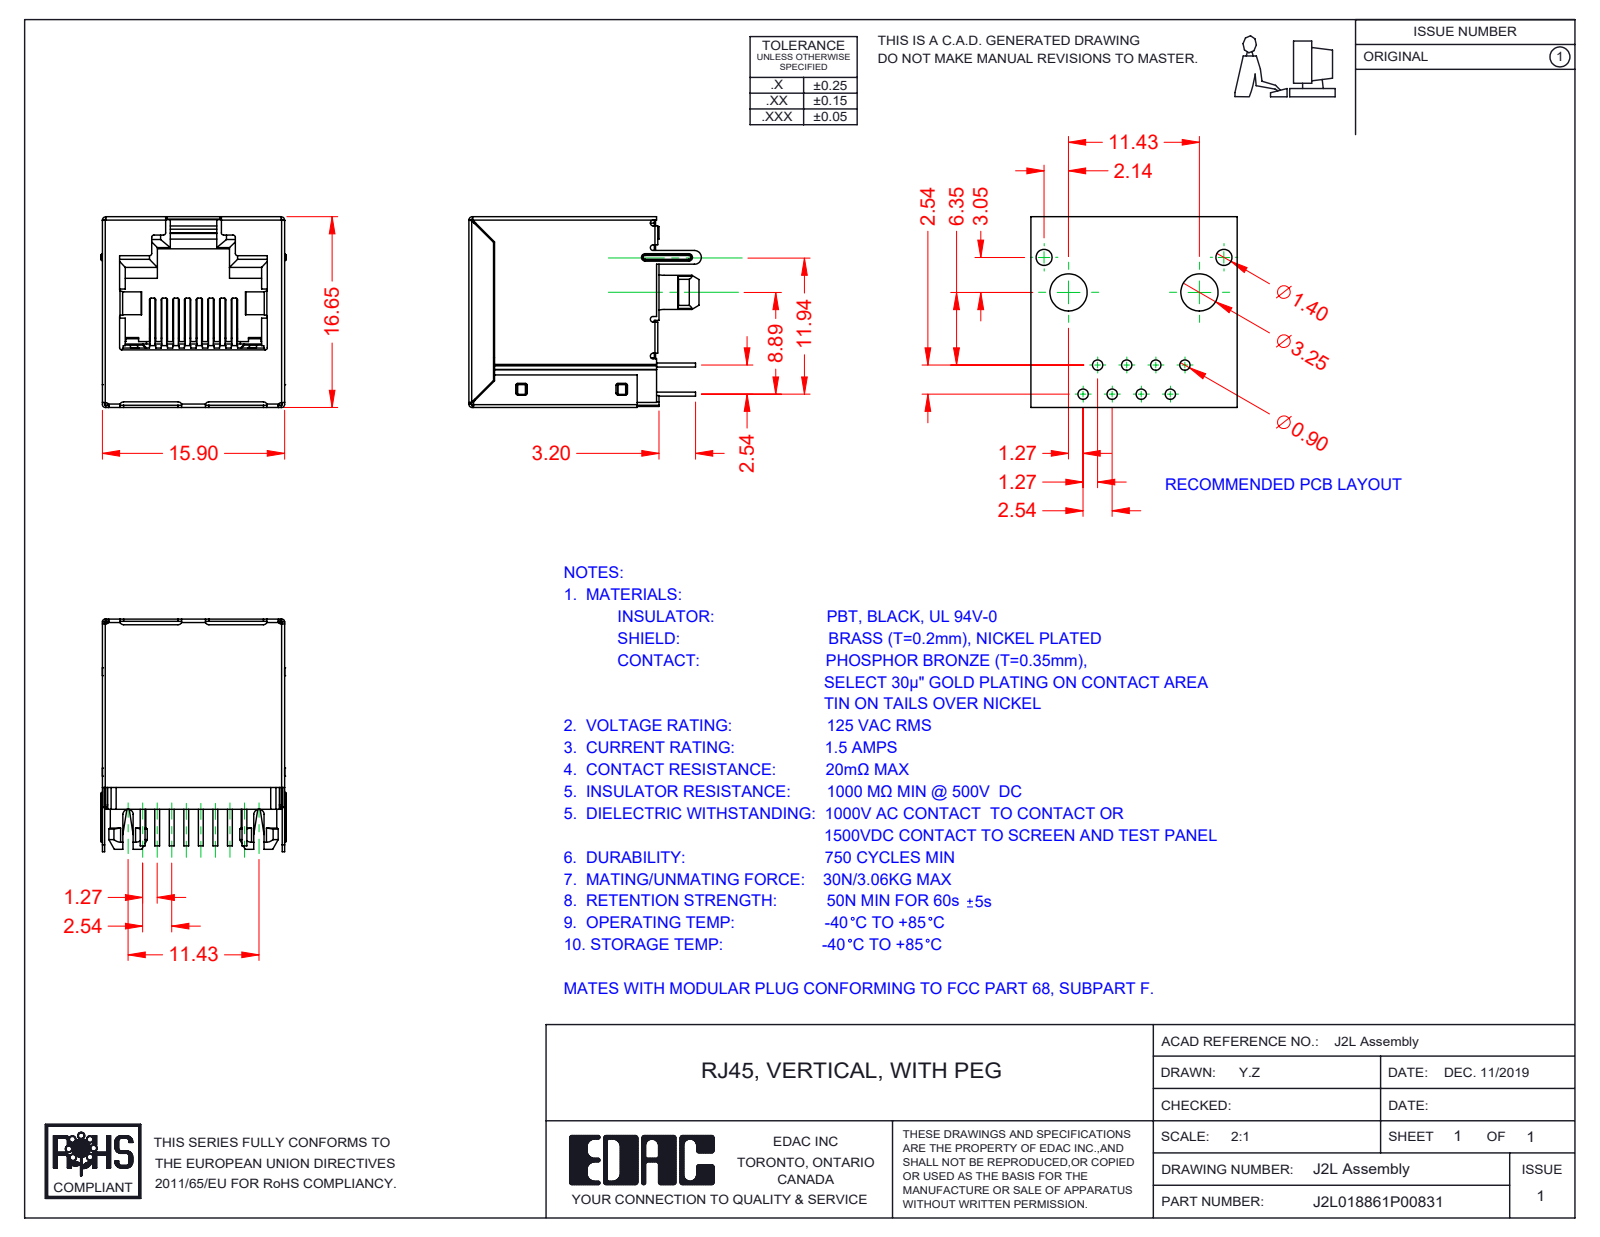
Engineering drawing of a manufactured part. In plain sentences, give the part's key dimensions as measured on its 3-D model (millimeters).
The part is named "2L Contact Lock; 2L Insulator; 2L Mylar Tape; 2L Shield (+2 more)". Its 3-D file was written by "SolidWorks 2016 (CONFIG_CONTROL_DESIGN)". It is 12 solids with 1131 faces: 784 planar, 284 cylindrical and 63 other. Overall it measures 20.3 by 16.65 by 16.2 millimeters. Its volume is 2 735 cubic millimeters and its surface area 6 843 square millimeters. Round bosses or shafts: 2 of diameter 3.1, 2 of diameter 1.1. Partial cylindrical surfaces (rounded edges, fillets, slot ends): 64 of radius 0.15, 20 of radius 0.25, 16 of radius 0.2, 14 of radius 0.3, 9 of radius 0.35, 8 of radius 0.1, 4 of radius 0.28, 3 of radius 0.5. The main face-to-face distances are 15.45, 15.7, 16.45, 16.2, 16.4, 15.65, 16.3, 16.25, 15.9, 15.5.
